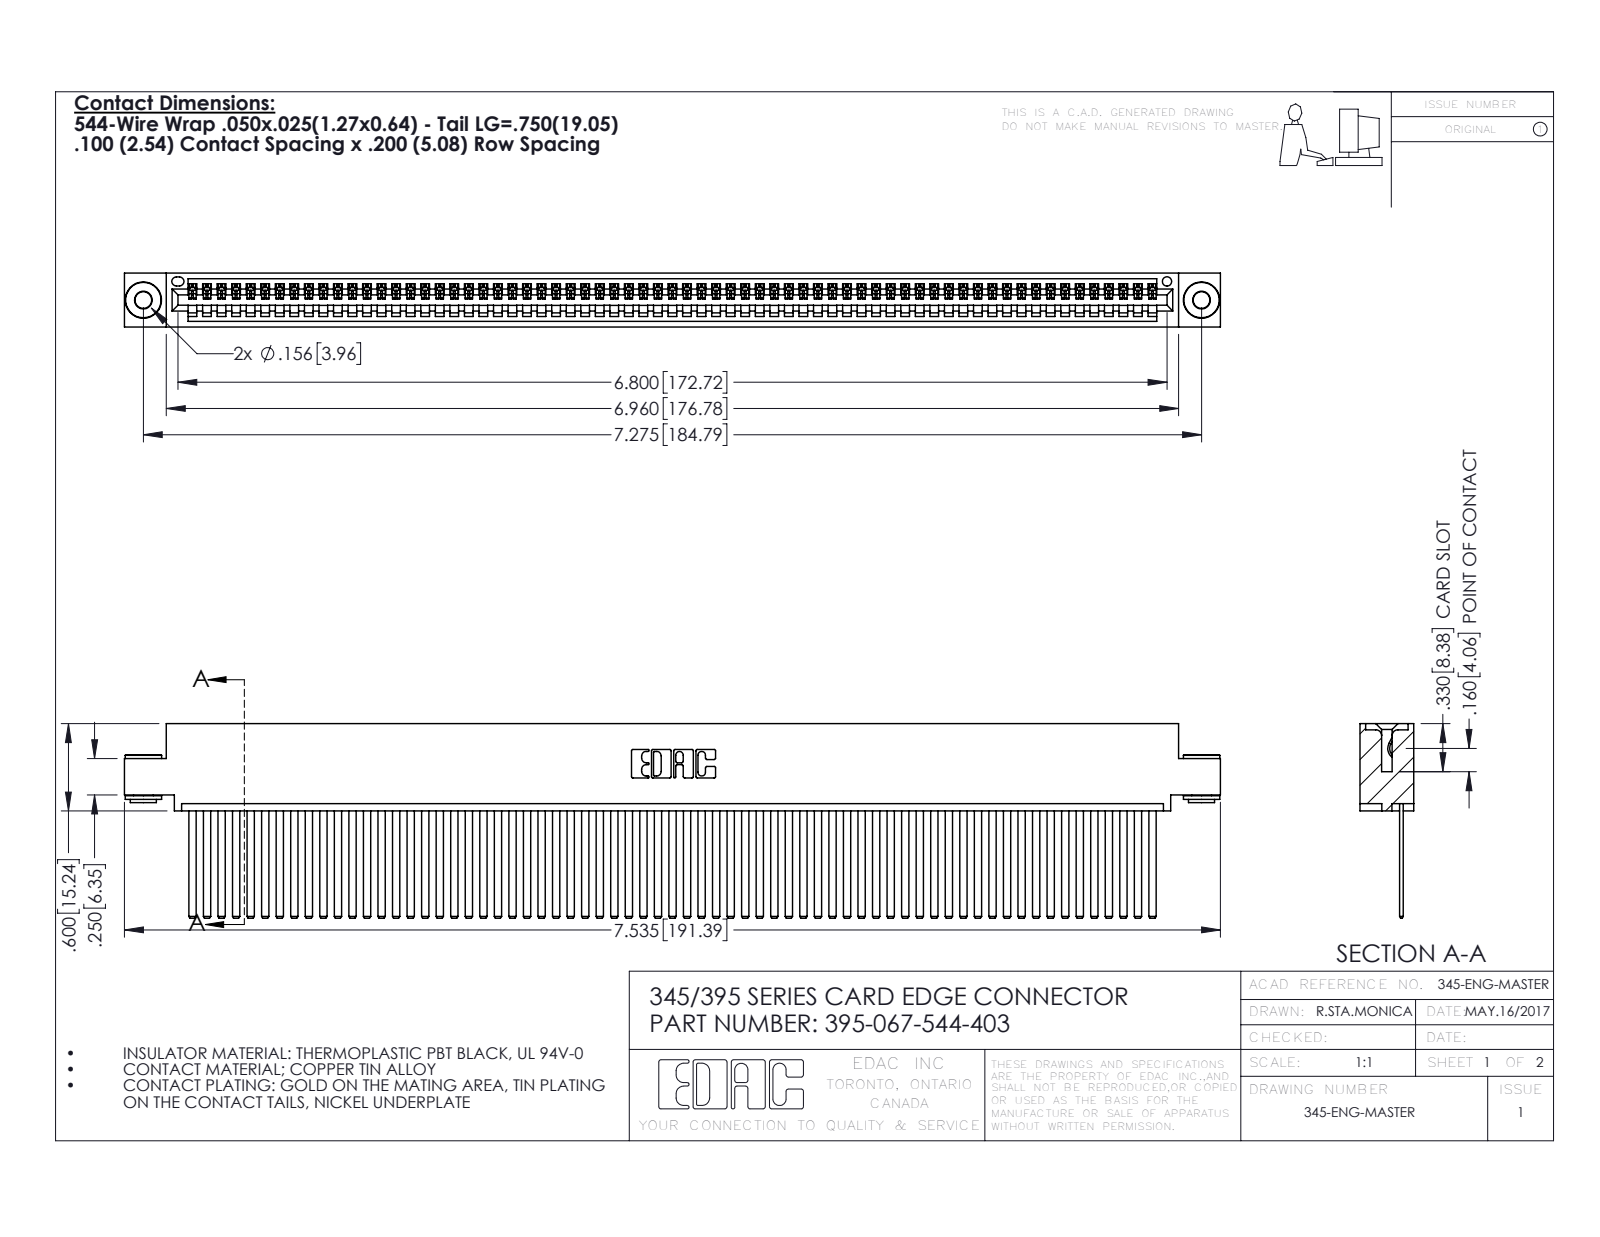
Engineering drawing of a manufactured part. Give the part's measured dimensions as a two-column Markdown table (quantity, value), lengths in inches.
| quantity | value |
| --- | --- |
| part name | 395-067-544-403; 345-250-002_345-250-002-102; 345-292-001_345-293-144; 345 Part_0.110 Offset - 0.156 Dia-TH |
| STEP written by | SolidWorks 2016 (CONFIG_CONTROL_DESIGN) |
| units | inches |
| bodies | 70 solids, 3652 faces (2506 planar, 1138 cylindrical, 8 other) |
| overall size | 7.535 × 1.337 × 0.37 |
| volume | 1.166 in³ |
| surface area | 43.95 in² |
| round holes (diameter × count) | 0.116 × 2, 0.156 × 2, 0.064 × 1 |
| round bosses / shafts (diameter × count) | 0.25 × 2, 0.18 × 2, 0.136 × 2 |
| partial cylindrical surfaces (radius × count) | 0.006 × 134, 0.01 × 22, 0.007 × 6, 0.031 × 6, 0.026 × 3, 0.031 × 2, 0.04 × 2, 0.014 × 1 |
| main face-to-face distances | 0.072, 0.298, 0.025, 0.098, 0.272, 0.37, 0.2, 0.225, 0.149, 0.072 |
| hole center spacings | 0.27, 7.039, 7.275 |
